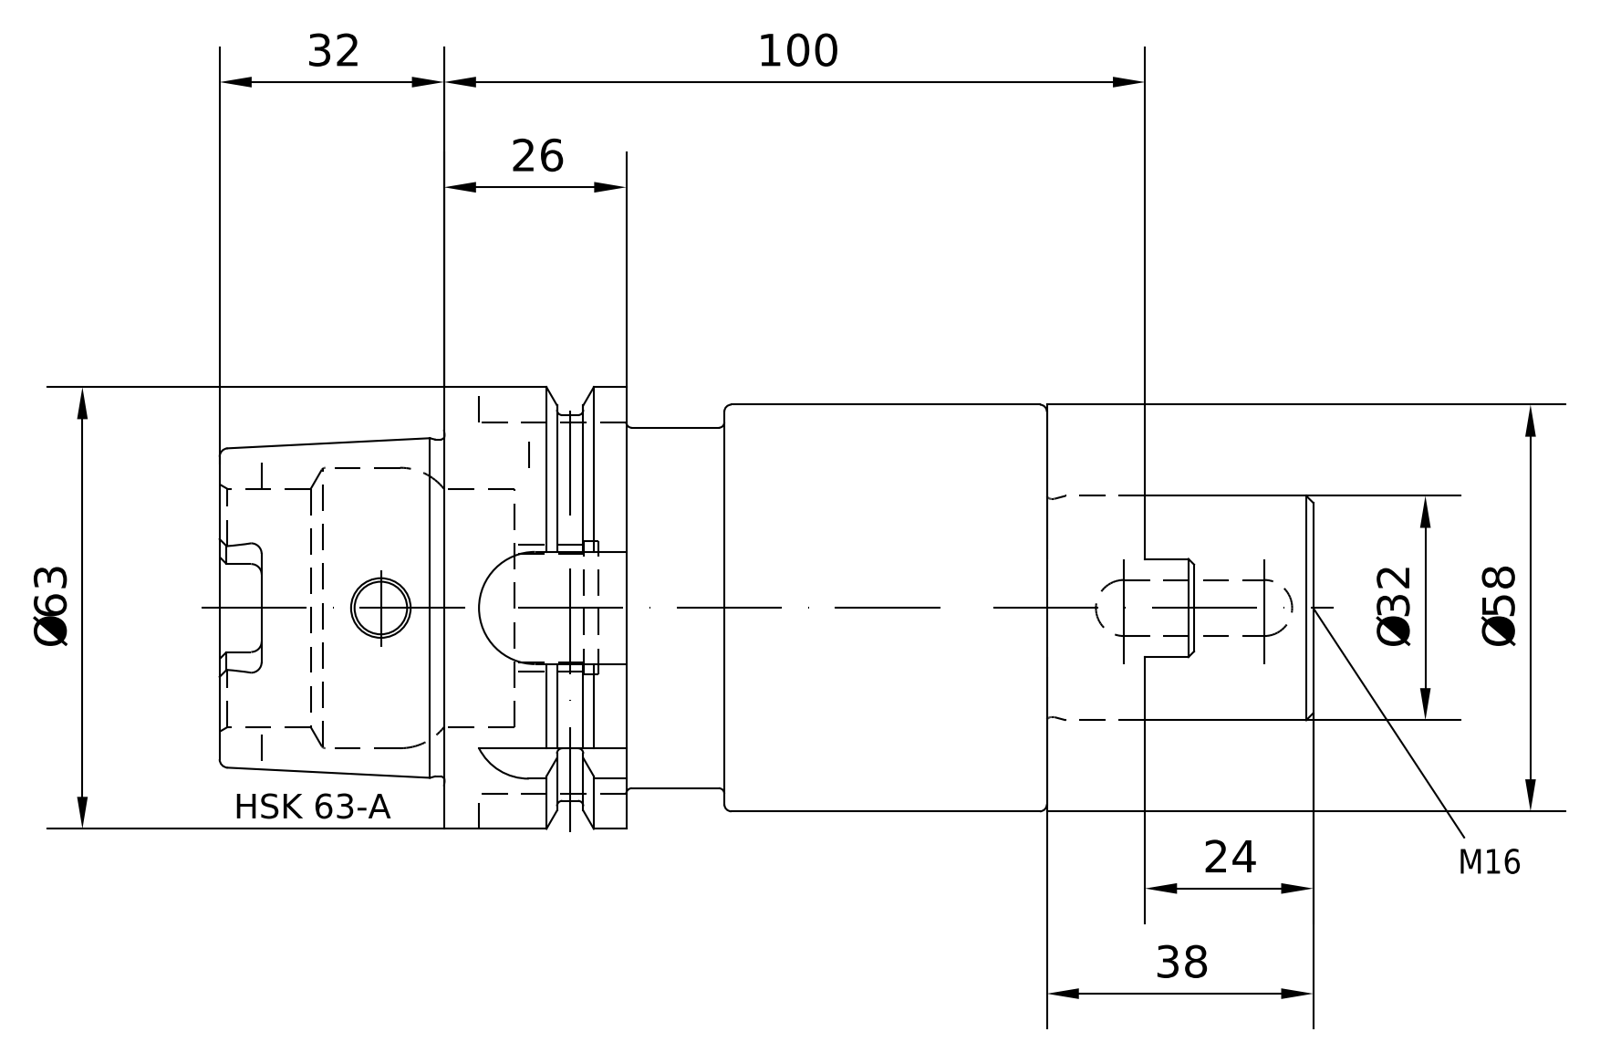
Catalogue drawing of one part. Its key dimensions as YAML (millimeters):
part_name: "A63-041-32; 85-200-32; A63-041-32_ASM"
step_written_by: "PRO/ENGINEER BY PARAMETRIC TECHNOLOGY CORPORATION, 2010430 (CONFIG_CONTROL_DESIGN)"
units: millimeters
bodies: {solids: 2, faces: 273, planar: 125, cylindrical: 66, other: 82}
overall_size: [156, 63, 63]
volume: 277030
surface_area: 51102
round_holes:
  - {diameter: 7.5, count: 1}
  - {diameter: 10, count: 1}
  - {diameter: 14, count: 1}
  - {diameter: 16, count: 1}
  - {diameter: 16.92, count: 1}
  - {diameter: 18.32, count: 1}
  - {diameter: 18.66, count: 1}
  - {diameter: 32.39, count: 1}
  - {diameter: 34, count: 1}
  - {diameter: 37, count: 1}
  - {diameter: 40, count: 1}
round_bosses_or_shafts:
  - {diameter: 63, count: 1}
  - {diameter: 58, count: 1}
  - {diameter: 55, count: 1}
  - {diameter: 51, count: 1}
  - {diameter: 48.04, count: 1}
  - {diameter: 32, count: 1}
  - {diameter: 18, count: 1}
partial_cylinders:
  - {radius: 1.5, count: 6}
  - {radius: 3, count: 4}
  - {radius: 4, count: 2}
  - {radius: 7.05, count: 1}
  - {radius: 8, count: 1}
  - {radius: 8.02, count: 1}
  - {radius: 9.02, count: 1}
face_to_face_distances: [14, 86, 100, 26, 60, 74, 10, 124, 98, 38]
